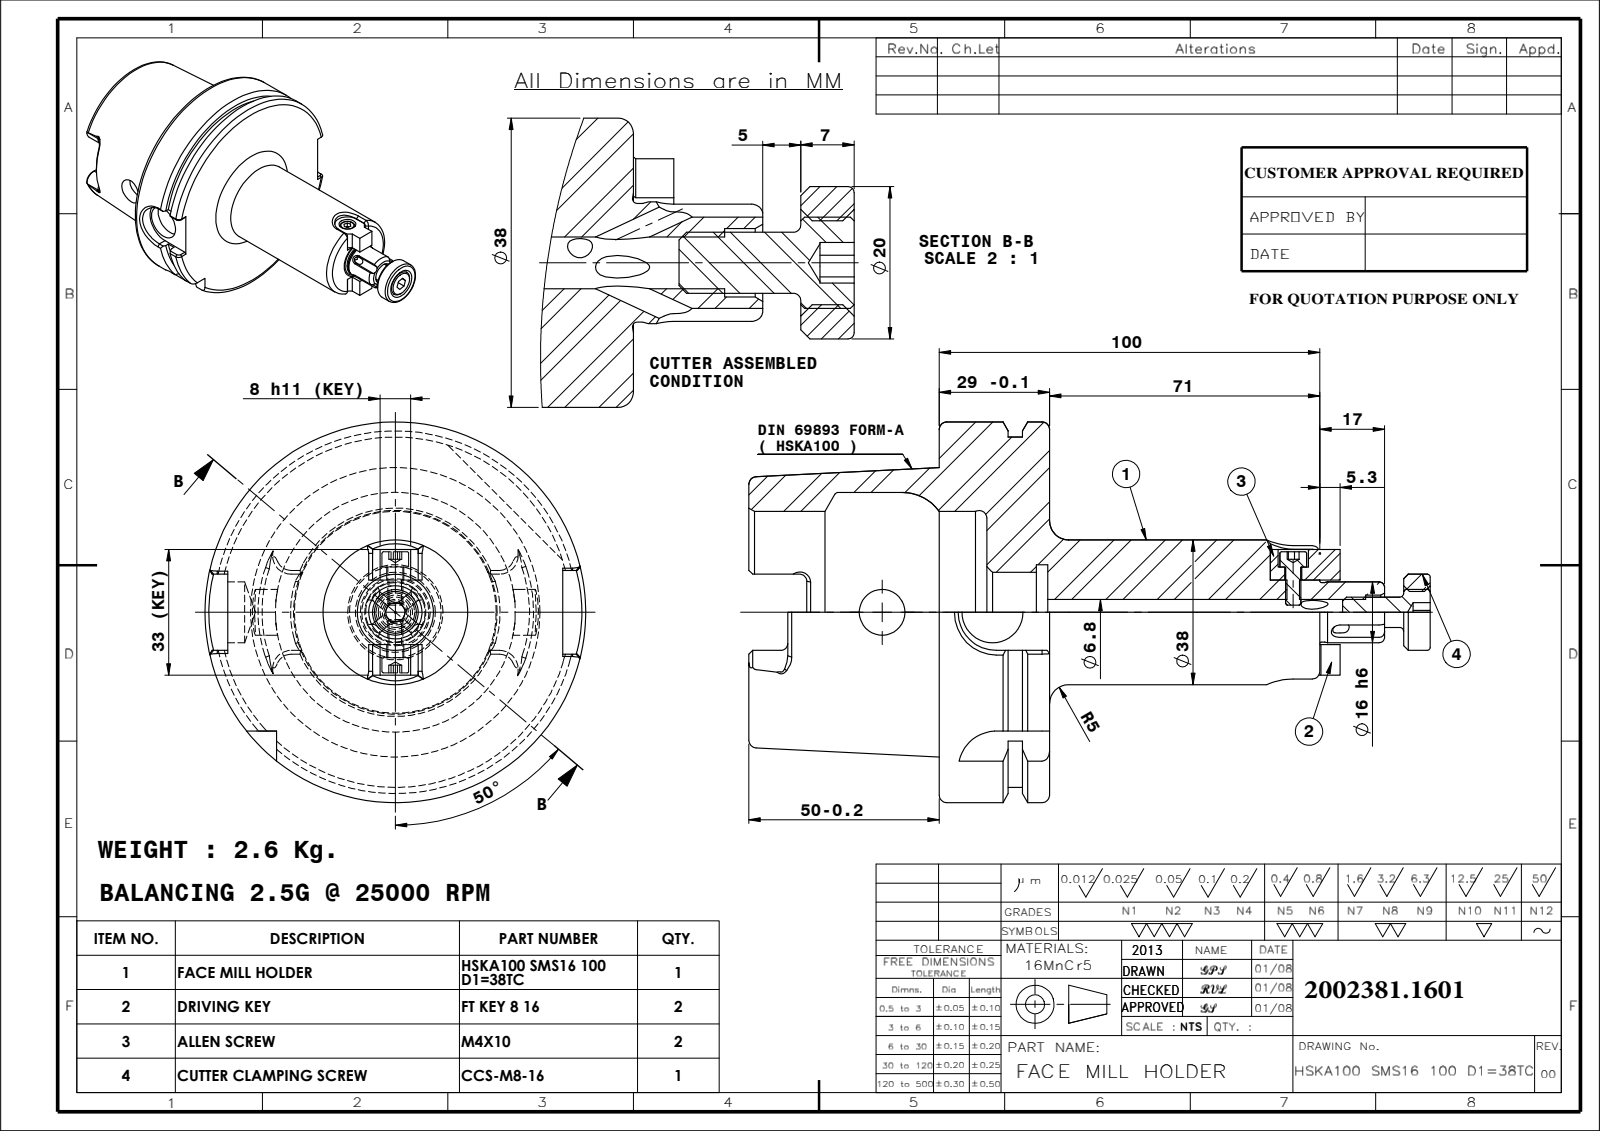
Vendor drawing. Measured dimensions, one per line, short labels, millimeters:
name: HSKA100 SMS16 100 D1=38TC; CCS-M8-16-2; M4X10_DIN 912 M4 x 10 --- 10N; FT KEY 8 16 (+2 more)
written by: SolidWorks 2009 (CONFIG_CONTROL_DESIGN)
unit: mm
bodies: 7 solids, 374 faces (144 planar, 98 cylindrical, 132 other)
size: 179 × 100 × 100
volume: 336 602 mm³; area: 65 493 mm²
holes: 4× ⌀3, 1× ⌀3.3, 1× ⌀4.5, 1× ⌀6.8, 1× ⌀8, 1× ⌀9, 1× ⌀11, 1× ⌀12, 1× ⌀16, 1× ⌀21, 1× ⌀25, 1× ⌀53
bosses: 1× ⌀100, 1× ⌀92, 1× ⌀38, 1× ⌀20, 1× ⌀16, 1× ⌀15.6, 1× ⌀12, 1× ⌀8
rounds: 6× R1.8, 4× R2, 4× R4.88, 2× R10, 1× R6, 1× R11
face distances: 29, 12.5, 16.5, 50, 62.5, 79, 100, 16, 78.5, 28.5
hole spacings: 29
